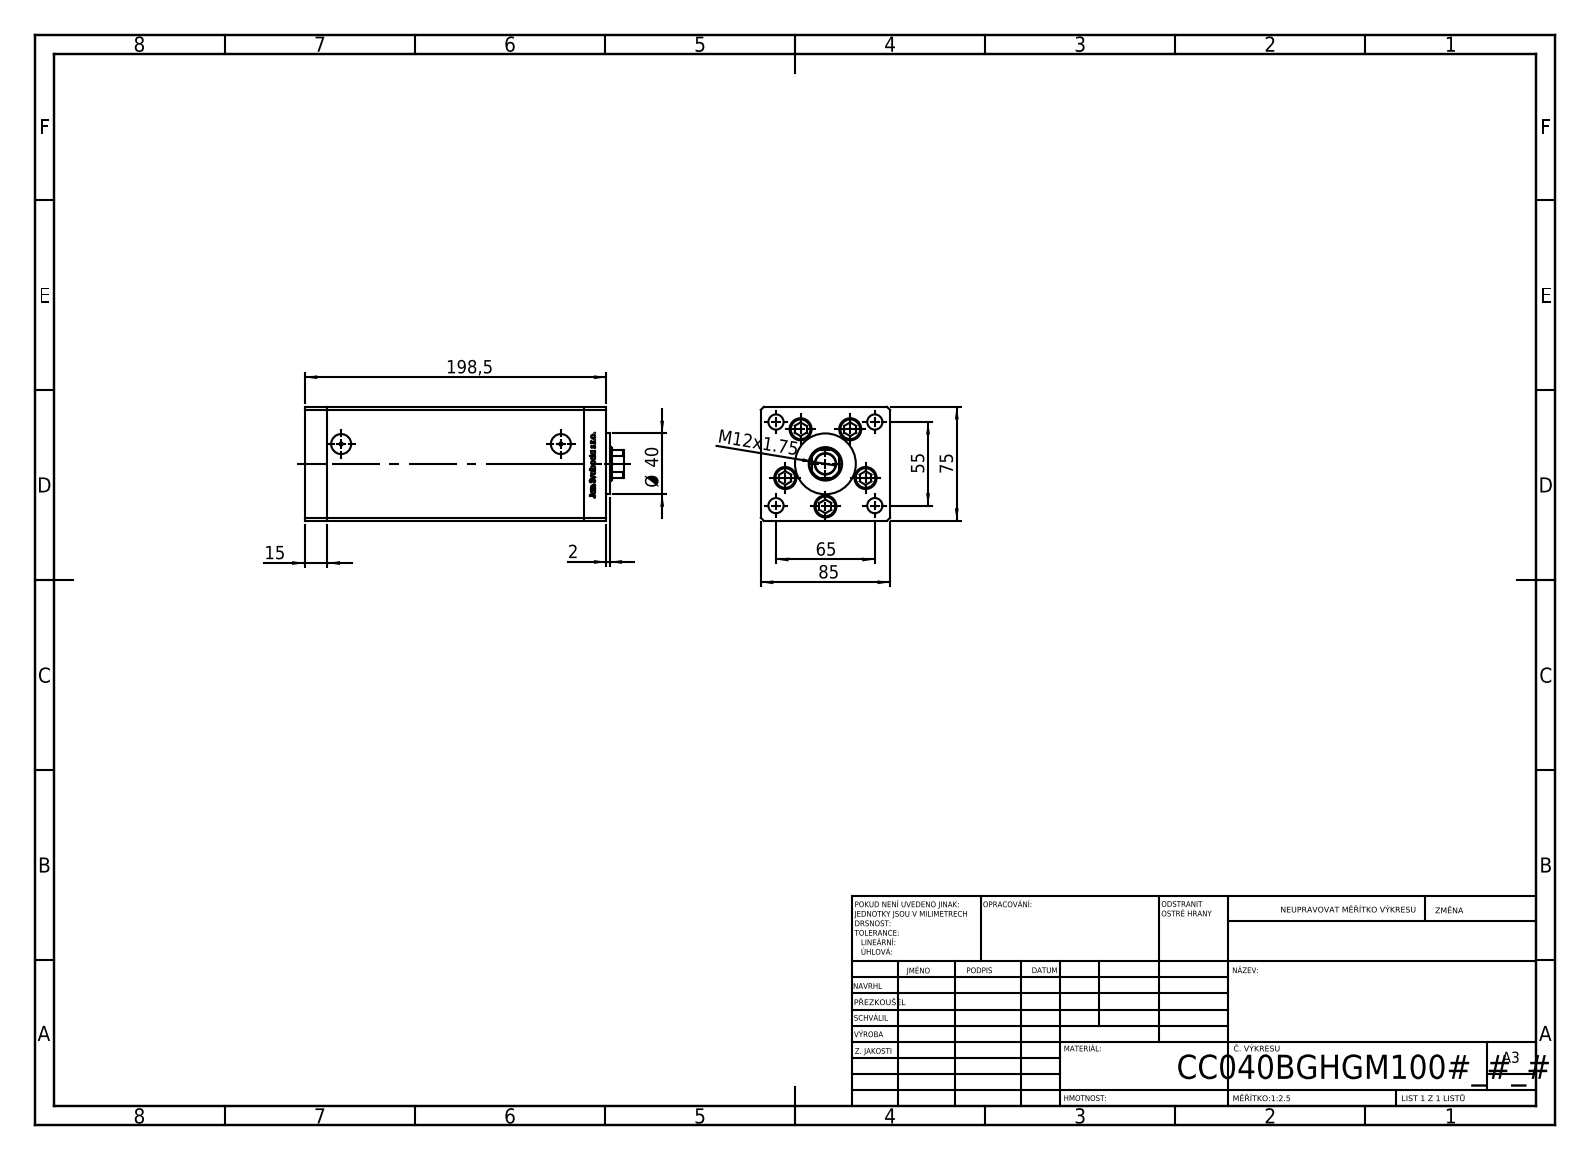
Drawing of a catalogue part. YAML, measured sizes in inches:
part_name: "V220C BACK_B; V220C_FRONT_B; V220C_B MIDDLE; ALLEN BOLT (+1 more)"
step_written_by: "SolidWorks 2019 (CONFIG_CONTROL_DESIGN)"
units: inches
bodies: {solids: 14, faces: 1183, planar: 462, cylindrical: 147, other: 574}
overall_size: [8.268, 3.346, 2.953]
volume: 68.22
surface_area: 265.3
round_holes:
  - {diameter: 0.433, count: 5}
  - {diameter: 0.571, count: 5}
  - {diameter: 0.394, count: 4}
  - {diameter: 0.079, count: 2}
  - {diameter: 0.518, count: 2}
  - {diameter: 0.531, count: 1}
  - {diameter: 0.866, count: 1}
round_bosses_or_shafts:
  - {diameter: 0.315, count: 5}
  - {diameter: 1.575, count: 1}
partial_cylinders:
  - {radius: 0.037, count: 2}
  - {radius: 0.413, count: 1}
face_to_face_distances: [3.346, 2.953, 0.591, 6.634, 7.224, 7.815, 1.348, 2.697, 0.758, 5.876]
hole_center_spacings: [1.102, 1.676, 0.664, 0.755, 1.273, 1.28, 1.324, 1.47]
